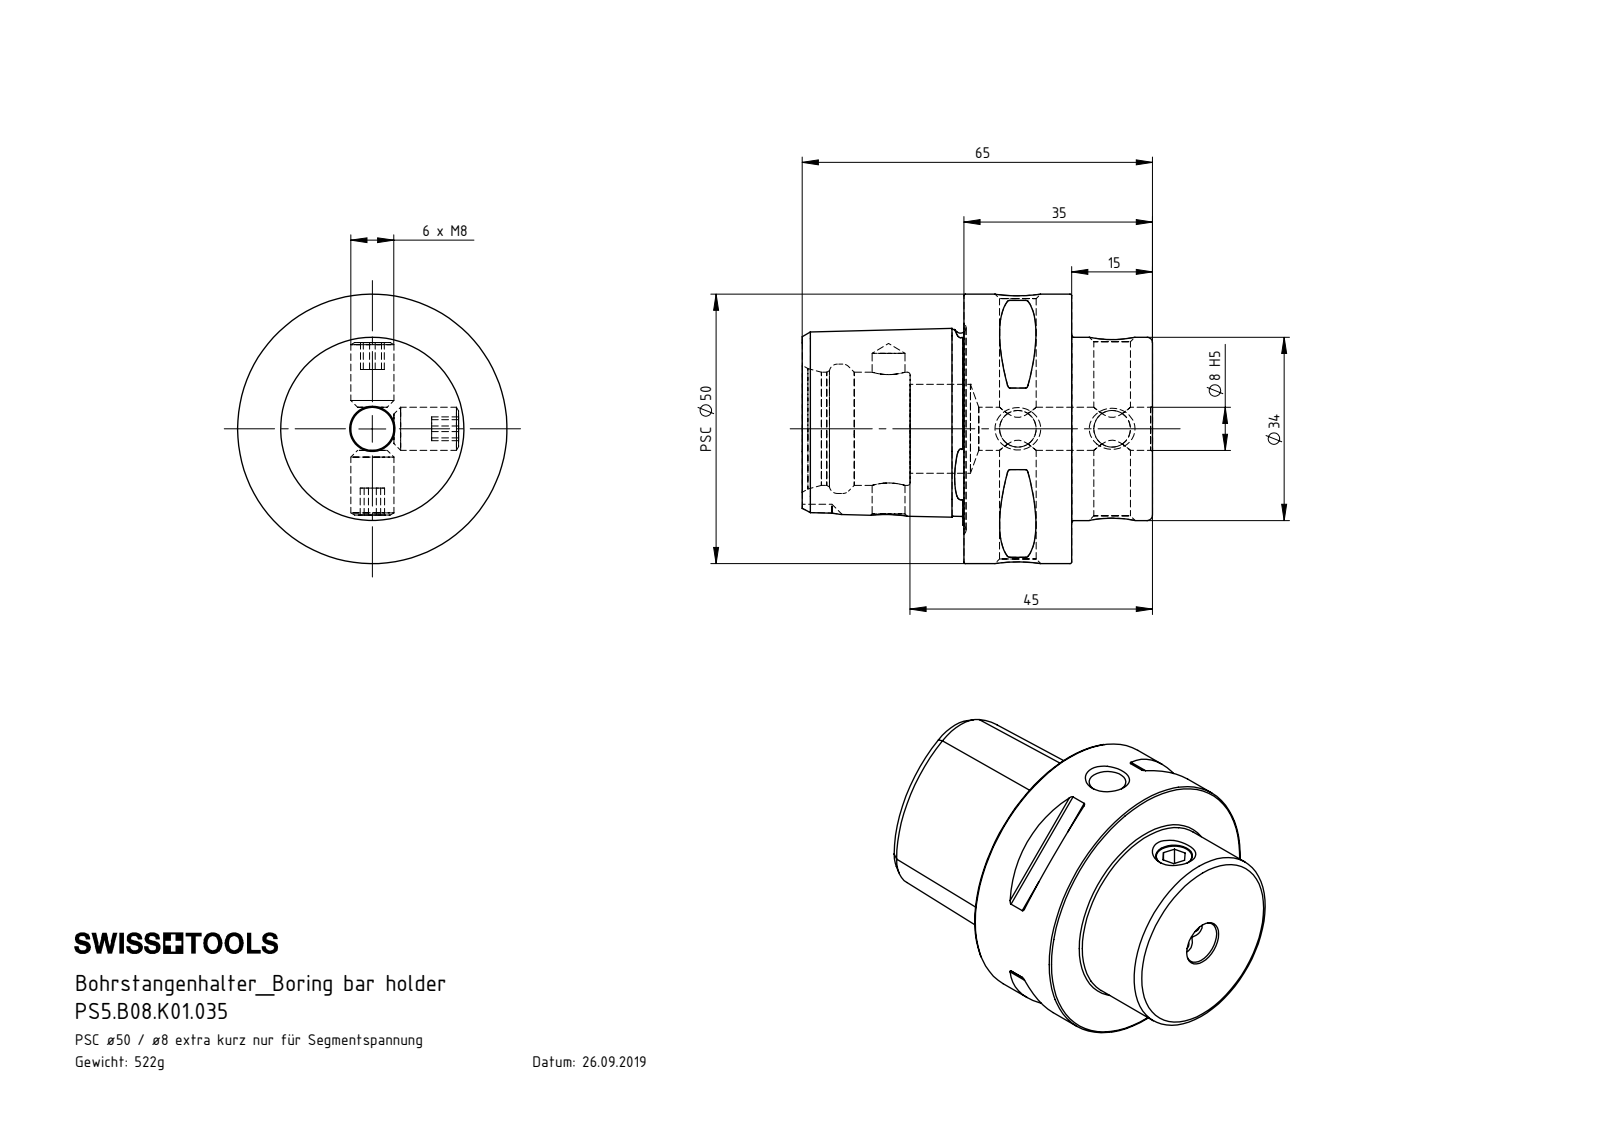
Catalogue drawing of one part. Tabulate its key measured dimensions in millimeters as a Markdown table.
| quantity | value |
| --- | --- |
| part name | ISO 4026 - M8 x 12_PreviewCfg; PS5.B08.K01.035; PS5-B08.K01.035_A |
| STEP written by | SolidWorks 2017 (AUTOMOTIVE_DESIGN) |
| units | millimeters |
| bodies | 7 solids, 171 faces (74 planar, 30 cylindrical, 67 other) |
| overall size | 65 × 50 × 50 |
| volume | 66 550 mm³ |
| surface area | 19 097 mm² |
| round holes (diameter × count) | 6.8 × 4, 6.1 × 1, 8 × 1, 16.5 × 1, 21 × 1, 24 × 1 |
| round bosses / shafts (diameter × count) | 8 × 4, 50 × 1, 34 × 1 |
| partial cylindrical surfaces (radius × count) | 0.5 × 8, 4 × 1 |
| main face-to-face distances | 20, 15, 35, 30, 50, 65, 4, 19.18, 44.4, 12 |
| hole center spacings | 17.5, 24, 41.5 |
